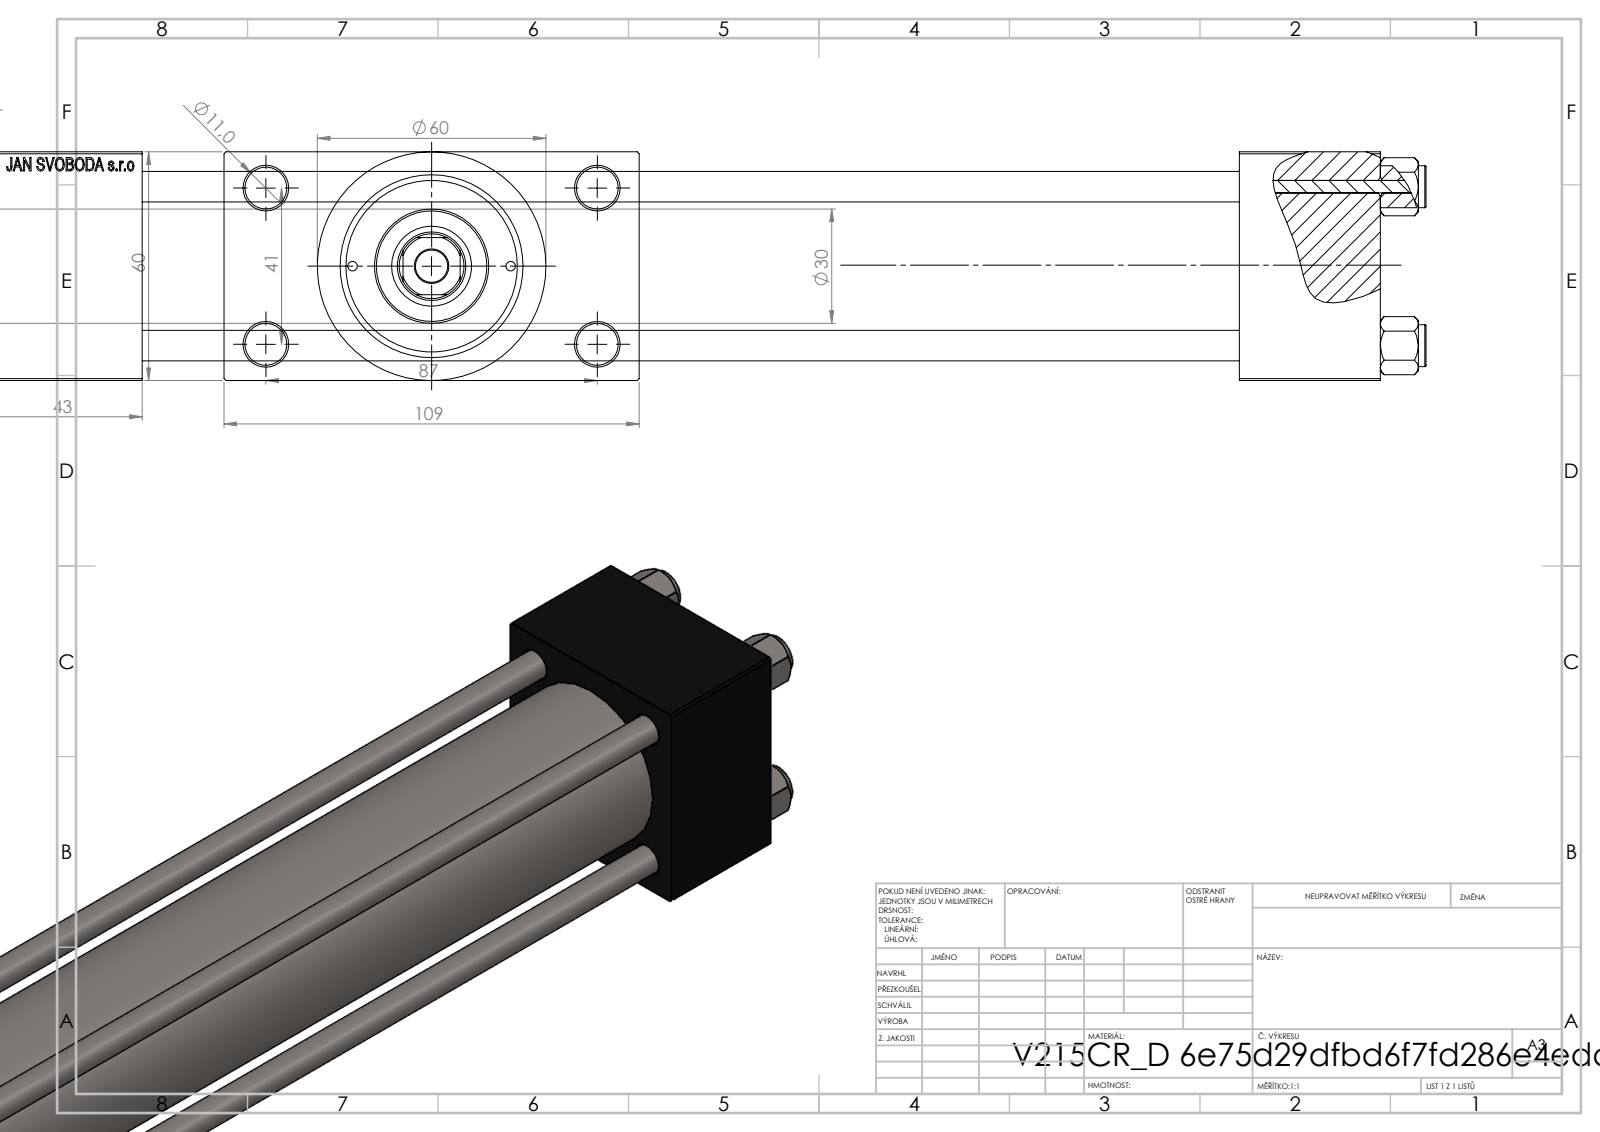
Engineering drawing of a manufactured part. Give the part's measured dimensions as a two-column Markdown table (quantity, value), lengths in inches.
| quantity | value |
| --- | --- |
| part name | V215CR_VCP_D; NUT_M5_D; V215CR_D_Body; V215CR_D_TYCINKA (+1 more) |
| STEP written by | SolidWorks 2019 (CONFIG_CONTROL_DESIGN) |
| units | inches |
| bodies | 11 solids, 1112 faces (500 planar, 92 cylindrical, 520 other) |
| overall size | 16.339 × 4.291 × 2.362 |
| volume | 43.34 in³ |
| surface area | 342.2 in² |
| round holes (diameter × count) | 0.315 × 4, 0.433 × 4, 0.098 × 2, 0.276 × 2, 0.656 × 2, 0.945 × 2, 0.335 × 1, 0.709 × 1, 0.827 × 1, 1.22 × 1, 1.575 × 1, 1.772 × 1 |
| round bosses / shafts (diameter × count) | 0.433 × 4, 2.362 × 1, 1.811 × 1, 1.181 × 1 |
| partial cylindrical surfaces (radius × count) | 0.335 × 1 |
| main face-to-face distances | 2.362, 11.339, 0.965, 3.327, 1.457, 12.795, 14.488, 13.031, 1.693, 13.179 |
| hole center spacings | 0.821, 0.892, 1.161, 1.206, 1.642, 1.832, 1.856, 1.893 |
